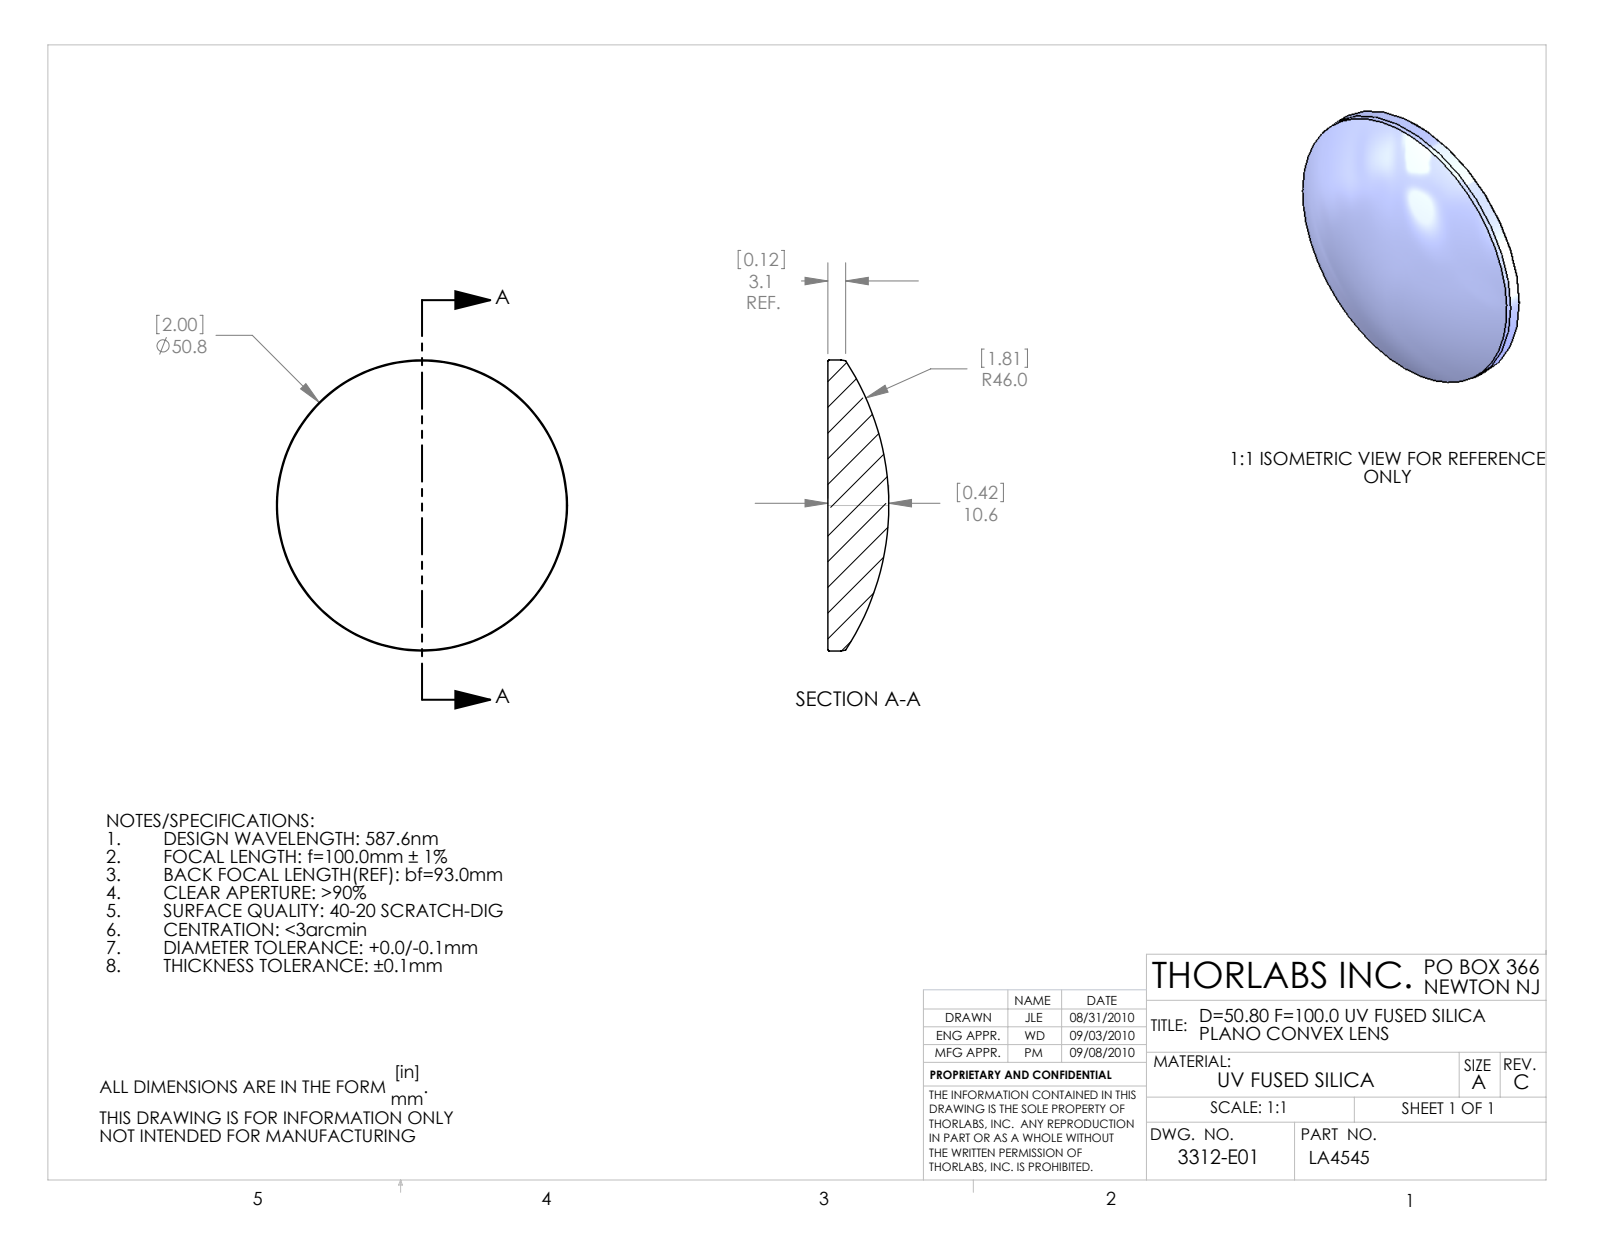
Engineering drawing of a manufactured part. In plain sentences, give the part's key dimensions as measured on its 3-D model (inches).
The part is named "3312-E0W". Its 3-D file was written by "SolidWorks 2009 (AUTOMOTIVE_DESIGN)". It is 1 solid with 9 faces: 1 planar, 2 cylindrical and 6 other. Overall it measures 2 by 2 by 0.419 inches. Its volume is 0.857 cubic inches and its surface area 7.262 square inches. Round bosses or shafts: 1 of diameter 2.
